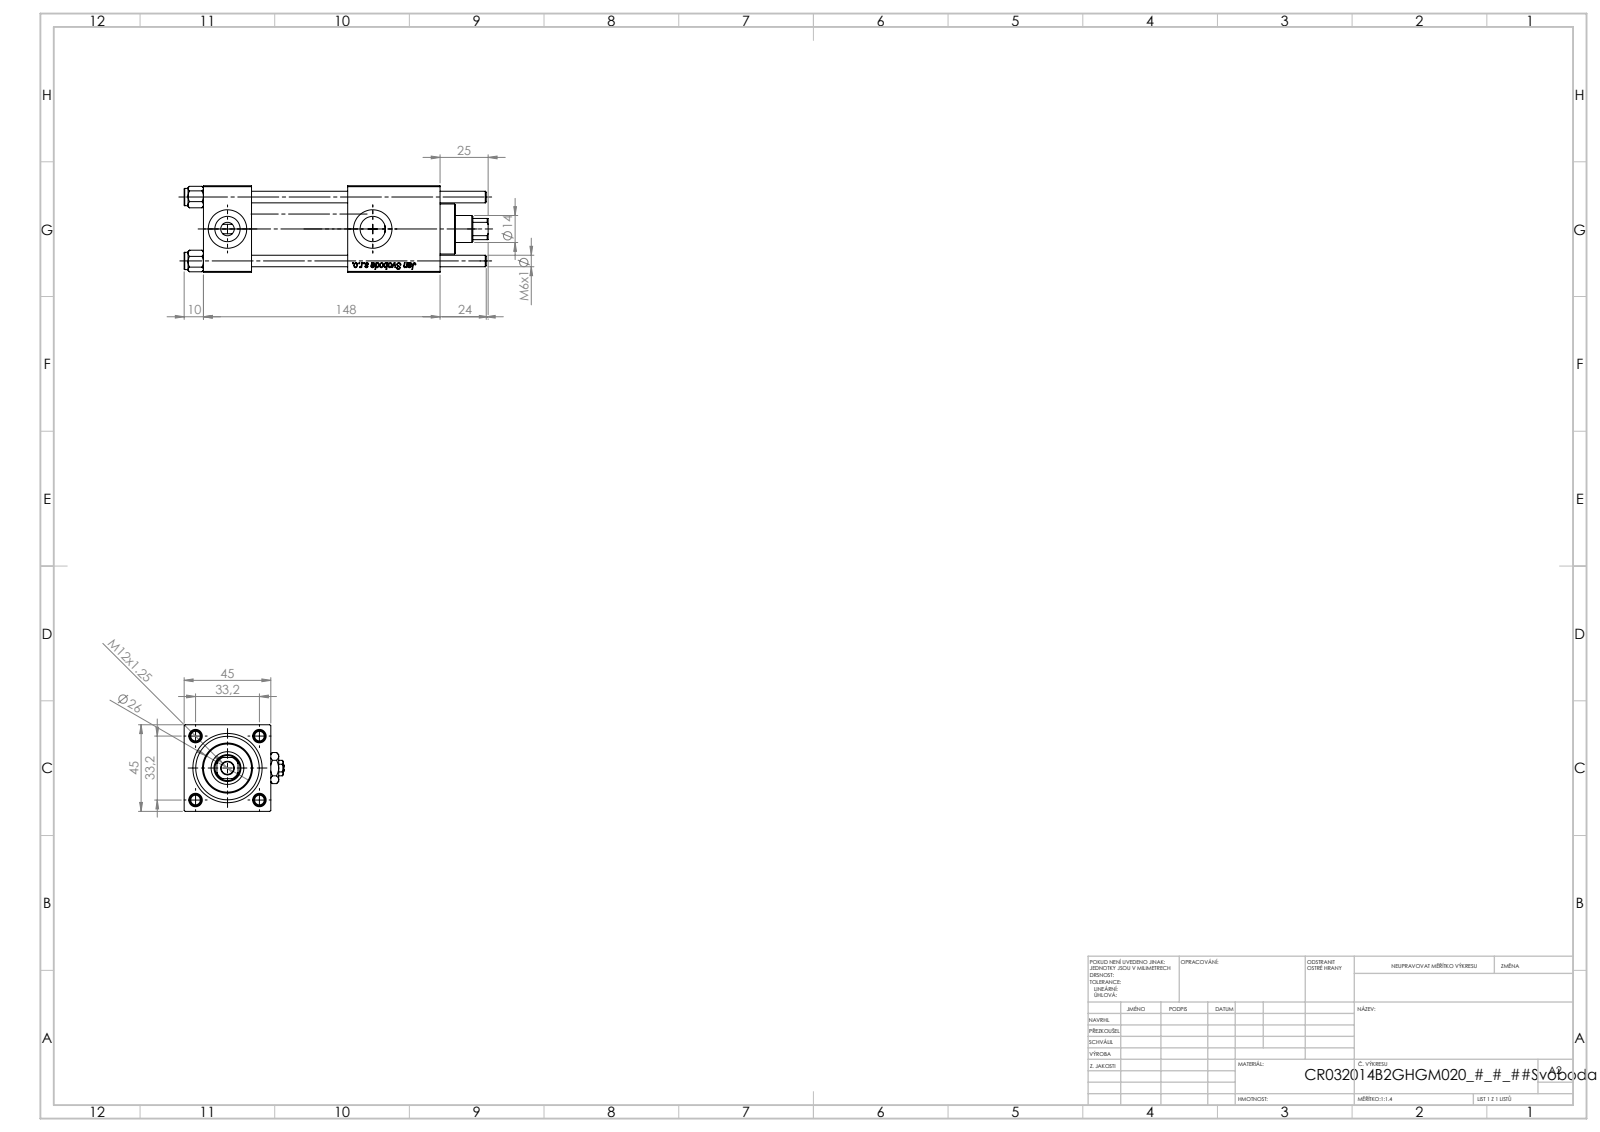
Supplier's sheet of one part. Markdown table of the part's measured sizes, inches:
| quantity | value |
| --- | --- |
| part name | Zatka_pro_OIL_PORT; V215CR_B-1; V215CR_VCP_B; NUT_M5_B (+2 more) |
| STEP written by | SolidWorks 2019 (CONFIG_CONTROL_DESIGN) |
| units | inches |
| bodies | 12 solids, 1208 faces (454 planar, 84 cylindrical, 670 other) |
| overall size | 6.22 × 2.047 × 1.772 |
| volume | 12.05 in³ |
| surface area | 114.2 in² |
| round holes (diameter × count) | 0.236 × 4, 0.276 × 2, 0.518 × 2, 0.787 × 2, 0.256 × 1, 0.551 × 1, 0.669 × 1, 0.945 × 1, 1.26 × 1, 1.299 × 1 |
| round bosses / shafts (diameter × count) | 0.354 × 4, 1.496 × 1, 1.024 × 1 |
| partial cylindrical surfaces (radius × count) | 0.256 × 1 |
| main face-to-face distances | 1.772, 0.984, 4.843, 3.858, 1.969, 2.953, 1.89, 3.713, 2.728, 0.76 |
| hole center spacings | 0.924, 1.307, 1.848, 2.972 |
